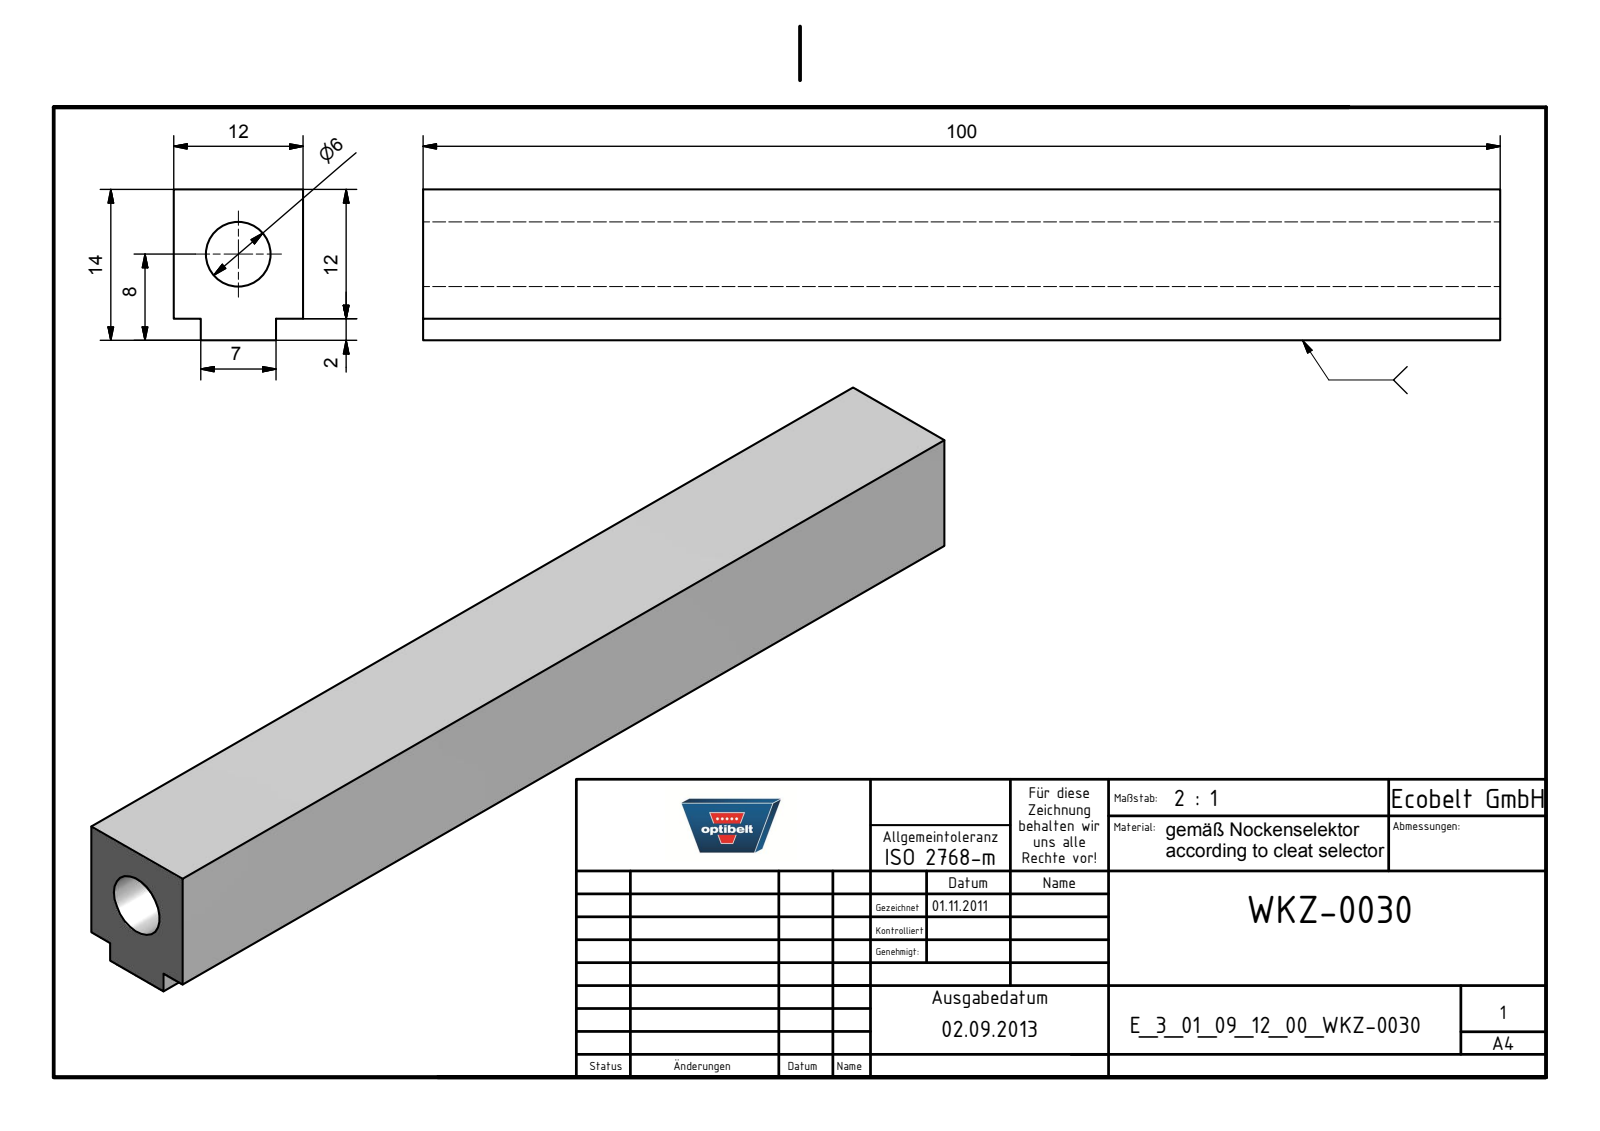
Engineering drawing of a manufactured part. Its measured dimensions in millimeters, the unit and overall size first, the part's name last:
Units: millimetres
Overall size (bounding box): 100 × 14 × 12
Round holes (diameter × count): ⌀6 ×1
Main face-to-face distances: 12, 14, 2, 2.5, 9.5, 7, 100
Volume: 12 973 mm³ · Surface area: 7 344 mm²
Bodies: 1 solid, 11 faces (10 planar, 1 cylindrical, 0 other)
Part name (STEP PRODUCT): E_3_01_09_12_00_WKZ-0030
STEP written by: Autodesk Inventor 2013 (AUTOMOTIVE_DESIGN)
